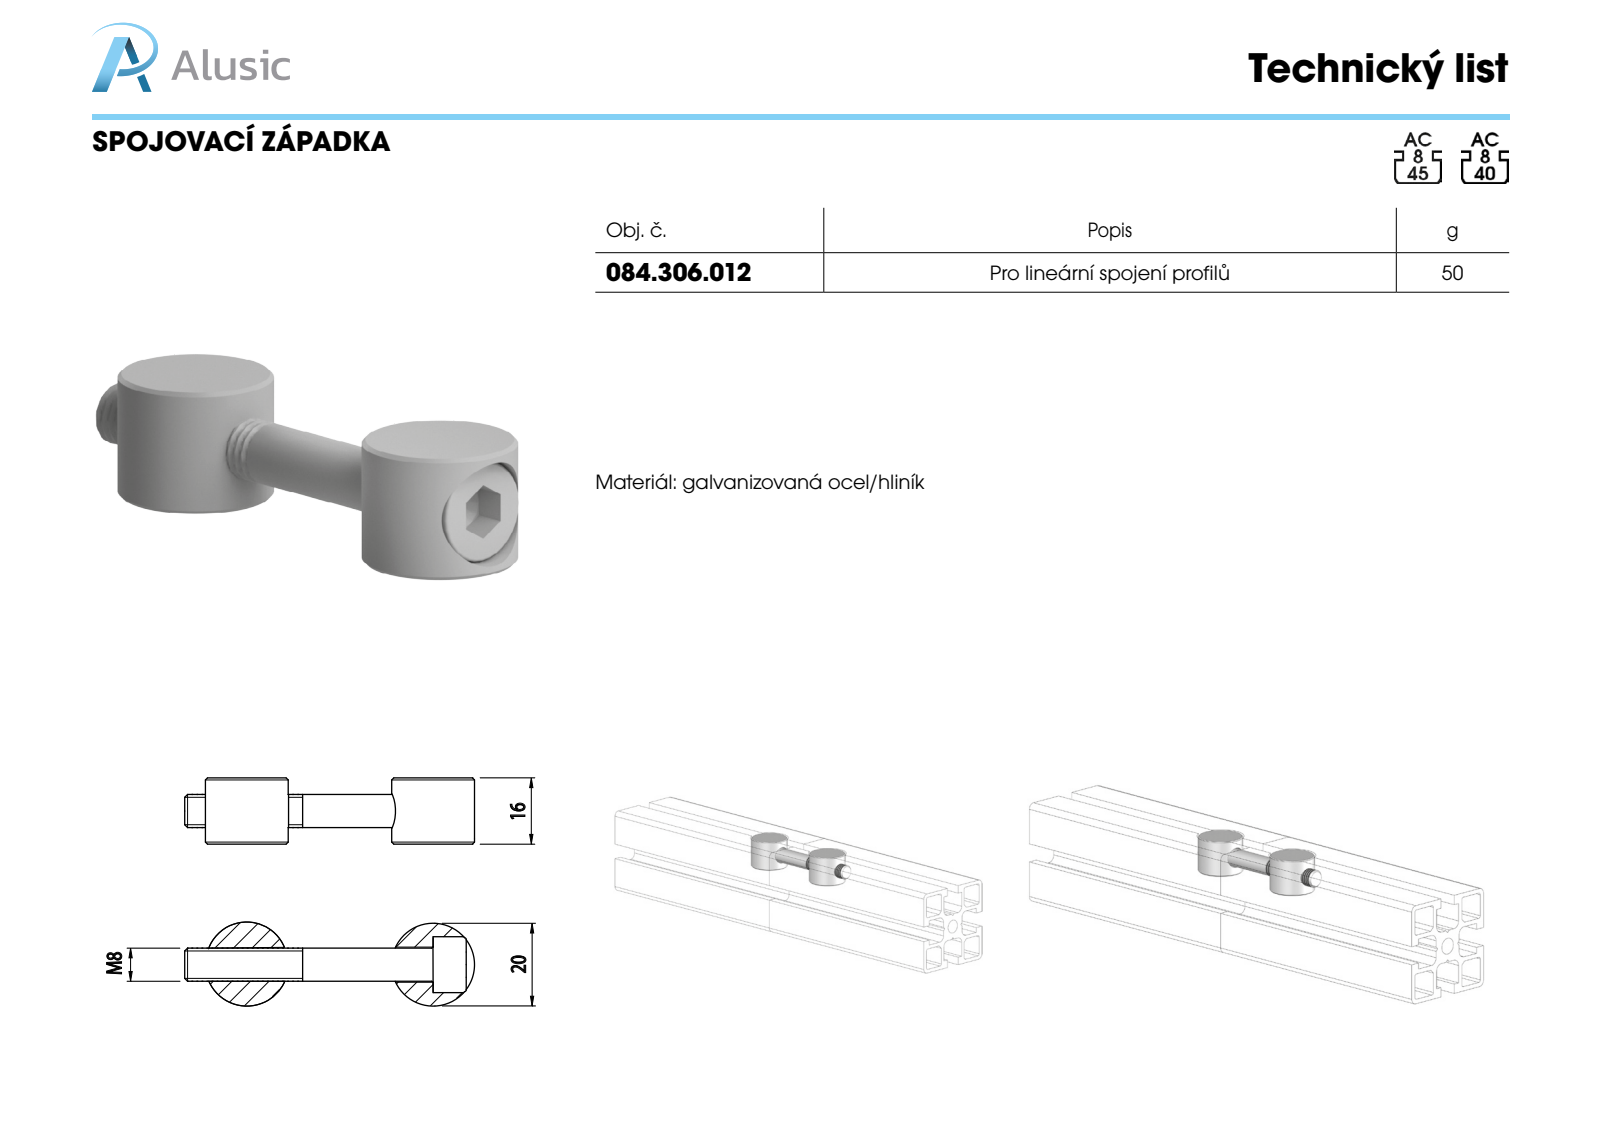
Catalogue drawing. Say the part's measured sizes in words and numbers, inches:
The part is named "084.306.012". Its 3-D file was written by "SolidWorks 2011 (CONFIG_CONTROL_DESIGN)". It is 1 solid with 10 faces: 2 planar, 4 cylindrical and 4 other. Overall it measures 0.787 by 0.787 by 0.63 inches. Its volume is 0.262 cubic inches and its surface area 3.002 square inches. Round holes: 1 of diameter 0.268. Round bosses or shafts: 1 of diameter 0.787. The main face-to-face distances are 0.63.
